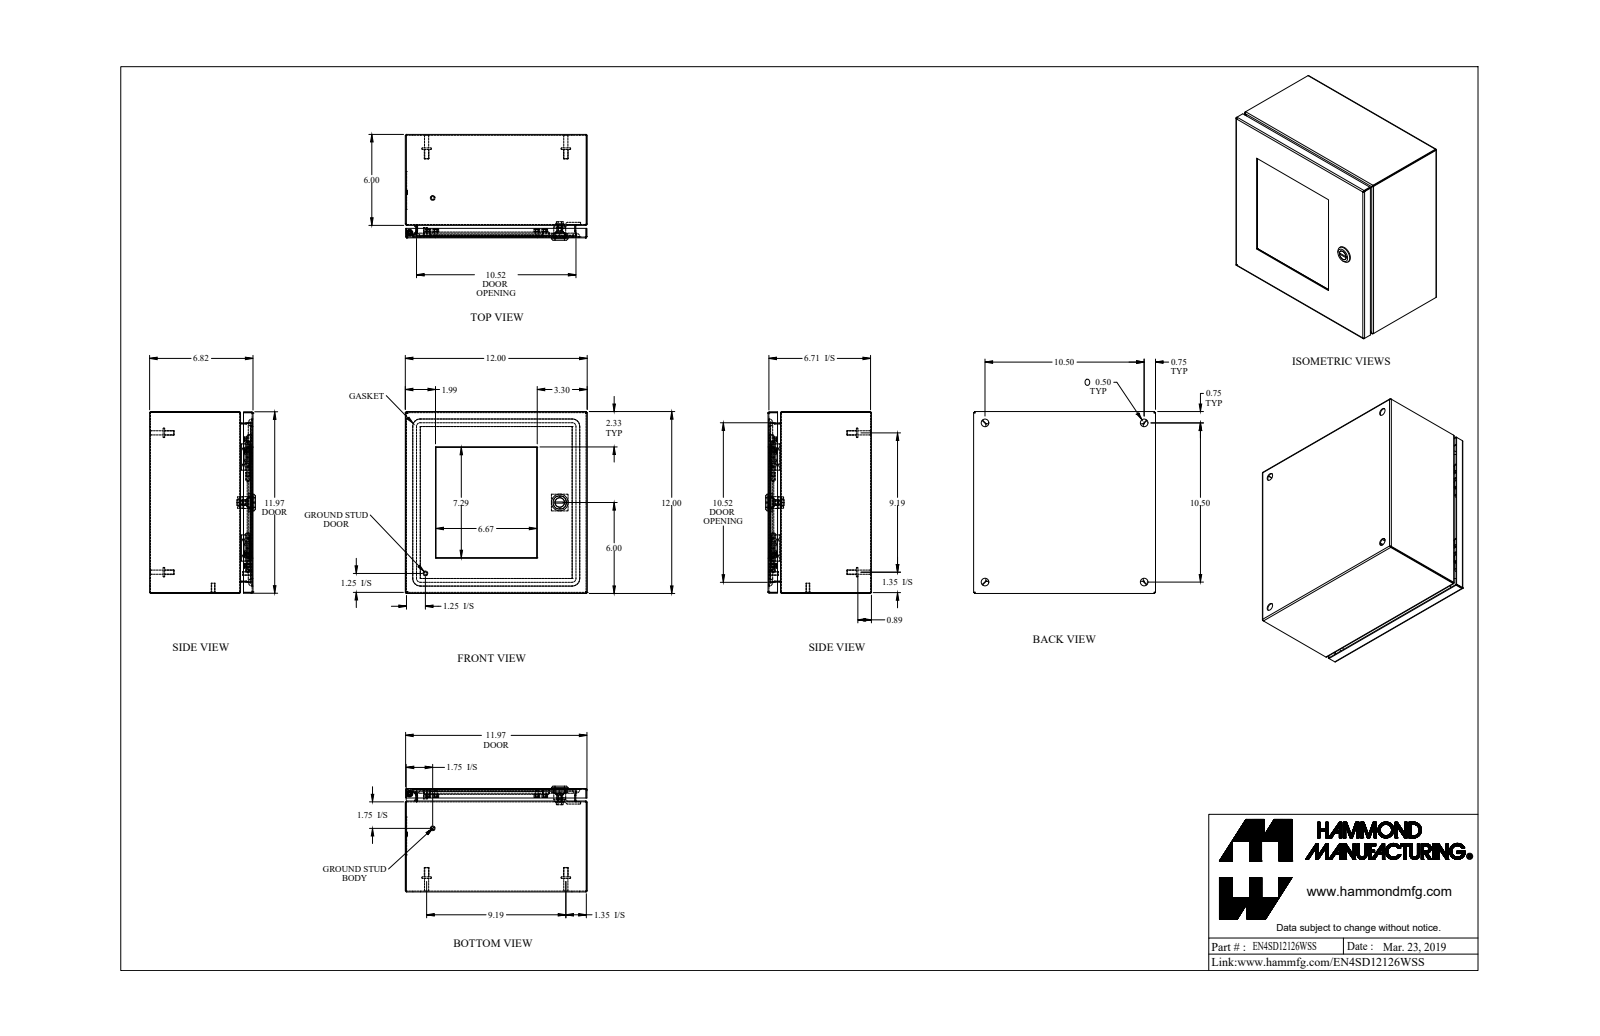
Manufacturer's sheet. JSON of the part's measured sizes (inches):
{"part_name": "EN4SD12126WSS_Default", "step_written_by": "SolidWorks 2019 (CONFIG_CONTROL_DESIGN)", "units": "inches", "bodies": {"solids": 47, "faces": 1015, "planar": 510, "cylindrical": 307, "other": 198}, "overall_size": [12, 12, 6.982], "volume_in3": 57.35, "surface_area_in2": 1573, "round_holes": [[0.13, 8], [0.25, 8], [0.5, 5], [0.172, 1], [0.197, 1], [0.24, 1], [0.242, 1], [0.387, 1], [0.63, 1], [0.768, 1]], "round_bosses_or_shafts": [[0.226, 9], [0.368, 8], [0.164, 8], [0.313, 6], [0.625, 5], [0.275, 4], [0.25, 2], [1.1, 1]], "partial_cylinders_radius": [[0.029, 21], [0.086, 21], [0.188, 12], [0.125, 10], [0.006, 4], [0.016, 4], [0.062, 4], [0.088, 4]], "face_to_face_distances": [0.057, 11.943, 6.765, 11.886, 6.708, 12, 6.822, 0.25, 0.307, 6.458], "hole_center_spacings": [6.875, 7.621, 7.623, 0.894, 0.895, 7.225, 7.228, 8.333]}
